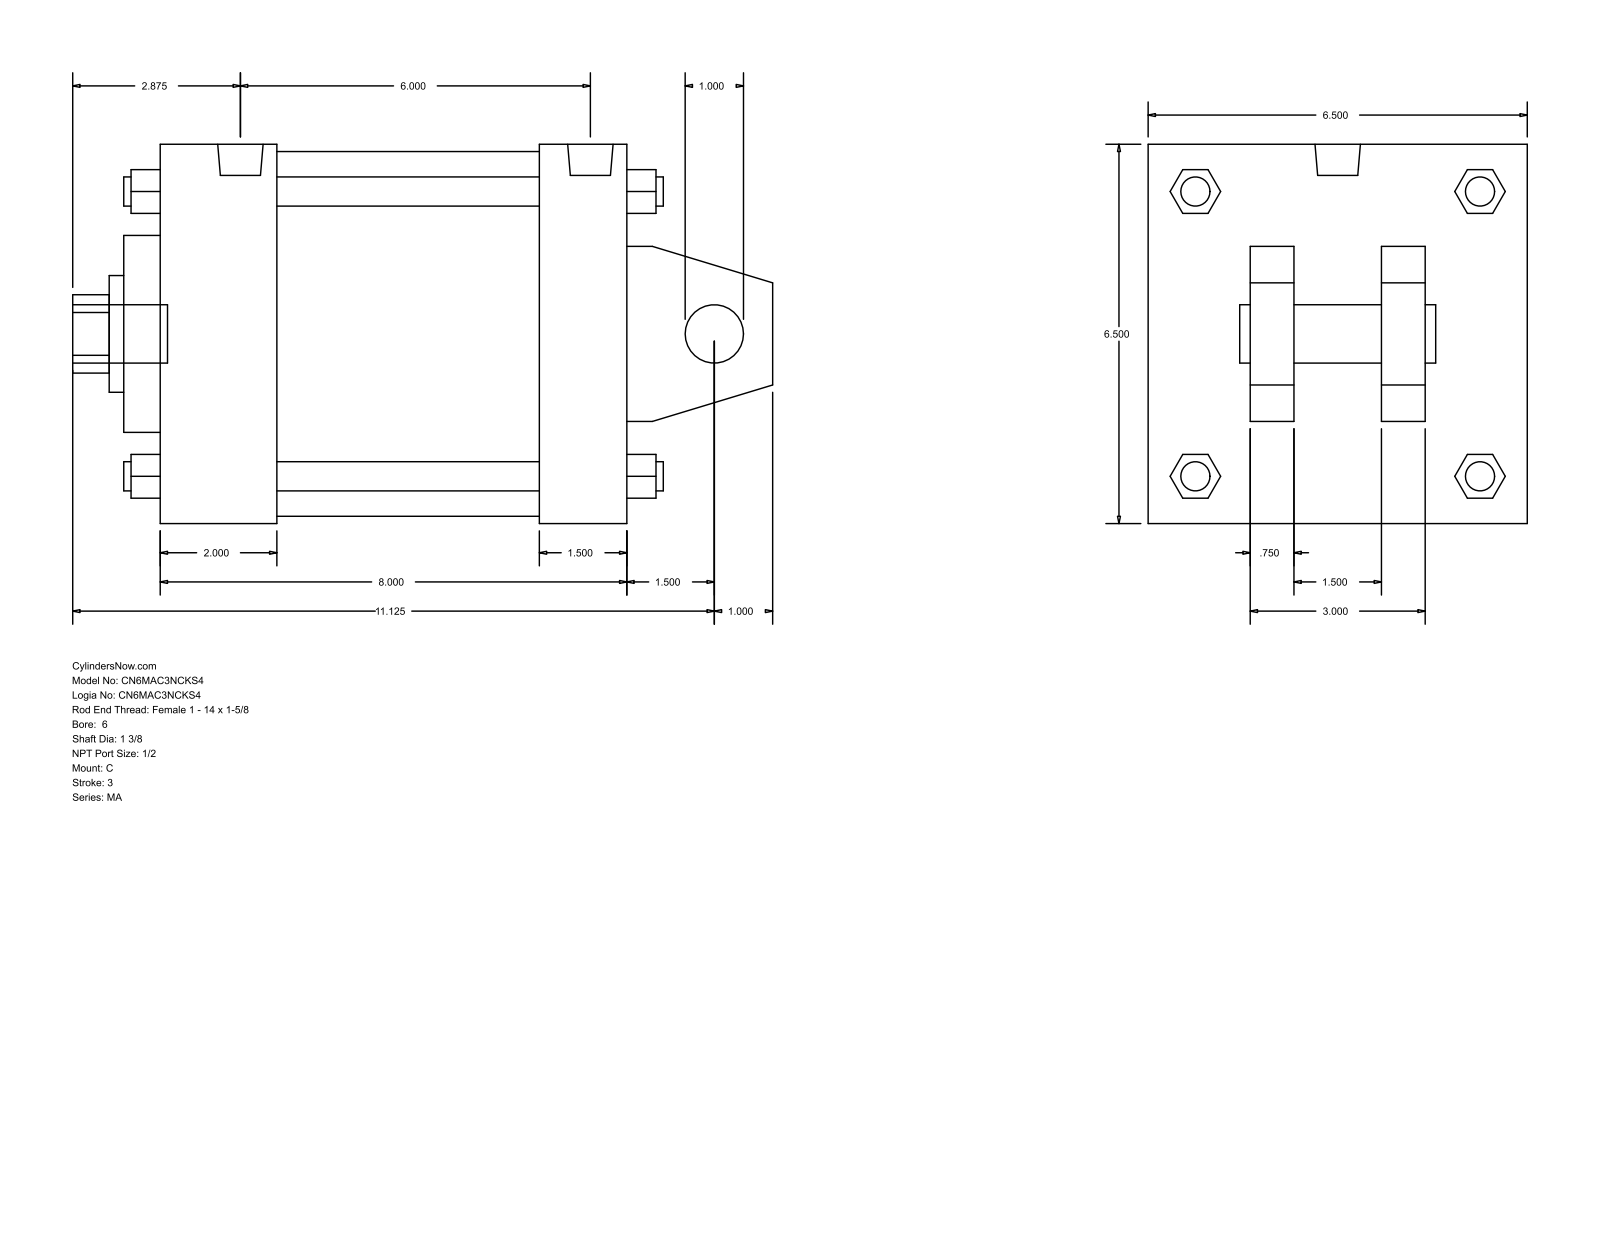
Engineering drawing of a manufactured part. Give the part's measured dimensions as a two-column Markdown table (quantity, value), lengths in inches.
| quantity | value |
| --- | --- |
| part name | MA_C__0600_1.375 |
| STEP written by | GSSL Pune (CONFIG_CONTROL_DESIGN) |
| units | inches |
| bodies | 0 solids, 141 faces (109 planar, 32 cylindrical, 0 other) |
| overall size | 12 × 6.5 × 6.5 |
| round holes (diameter × count) | 1 × 1, 1.375 × 1, 2 × 1, 3.375 × 1, 6.25 × 1 |
| round bosses / shafts (diameter × count) | 0.687 × 4, 0.5 × 4, 0.778 × 2, 1 × 1 |
| partial cylindrical surfaces (radius × count) | 0.672 × 1 |
| main face-to-face distances | 6.5, 8, 1.5, 0.75, 2.5, 4, 2, 1.75, 4.75, 2.25 |
